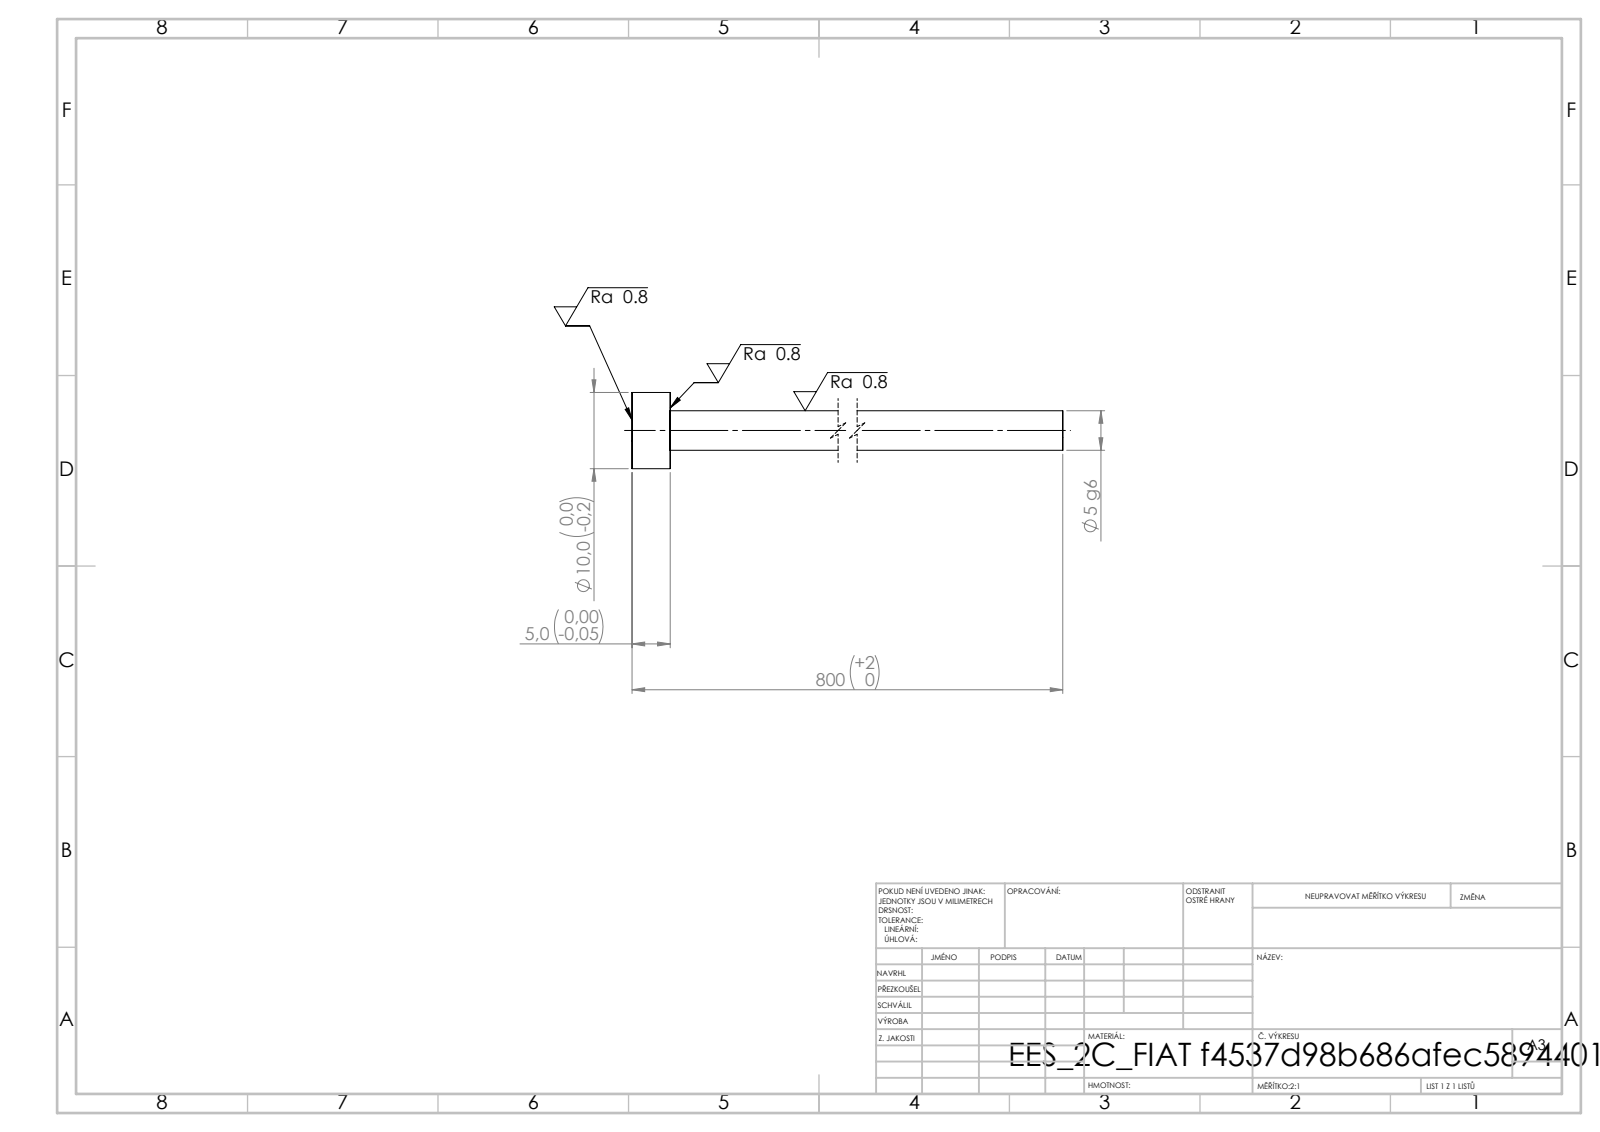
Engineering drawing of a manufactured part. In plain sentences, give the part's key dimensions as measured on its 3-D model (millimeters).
Its 3-D file was written by "SolidWorks 2019 (CONFIG_CONTROL_DESIGN)". It is 1 solid with 7 faces: 3 planar, 4 cylindrical and 0 other. Overall it measures 800 by 10 by 10 millimeters. Its volume is 17 276 cubic millimeters and its surface area 13 302 square millimeters. Round bosses or shafts: 1 of diameter 10, 1 of diameter 5.2. The main face-to-face distances are 5, 800, 795.
